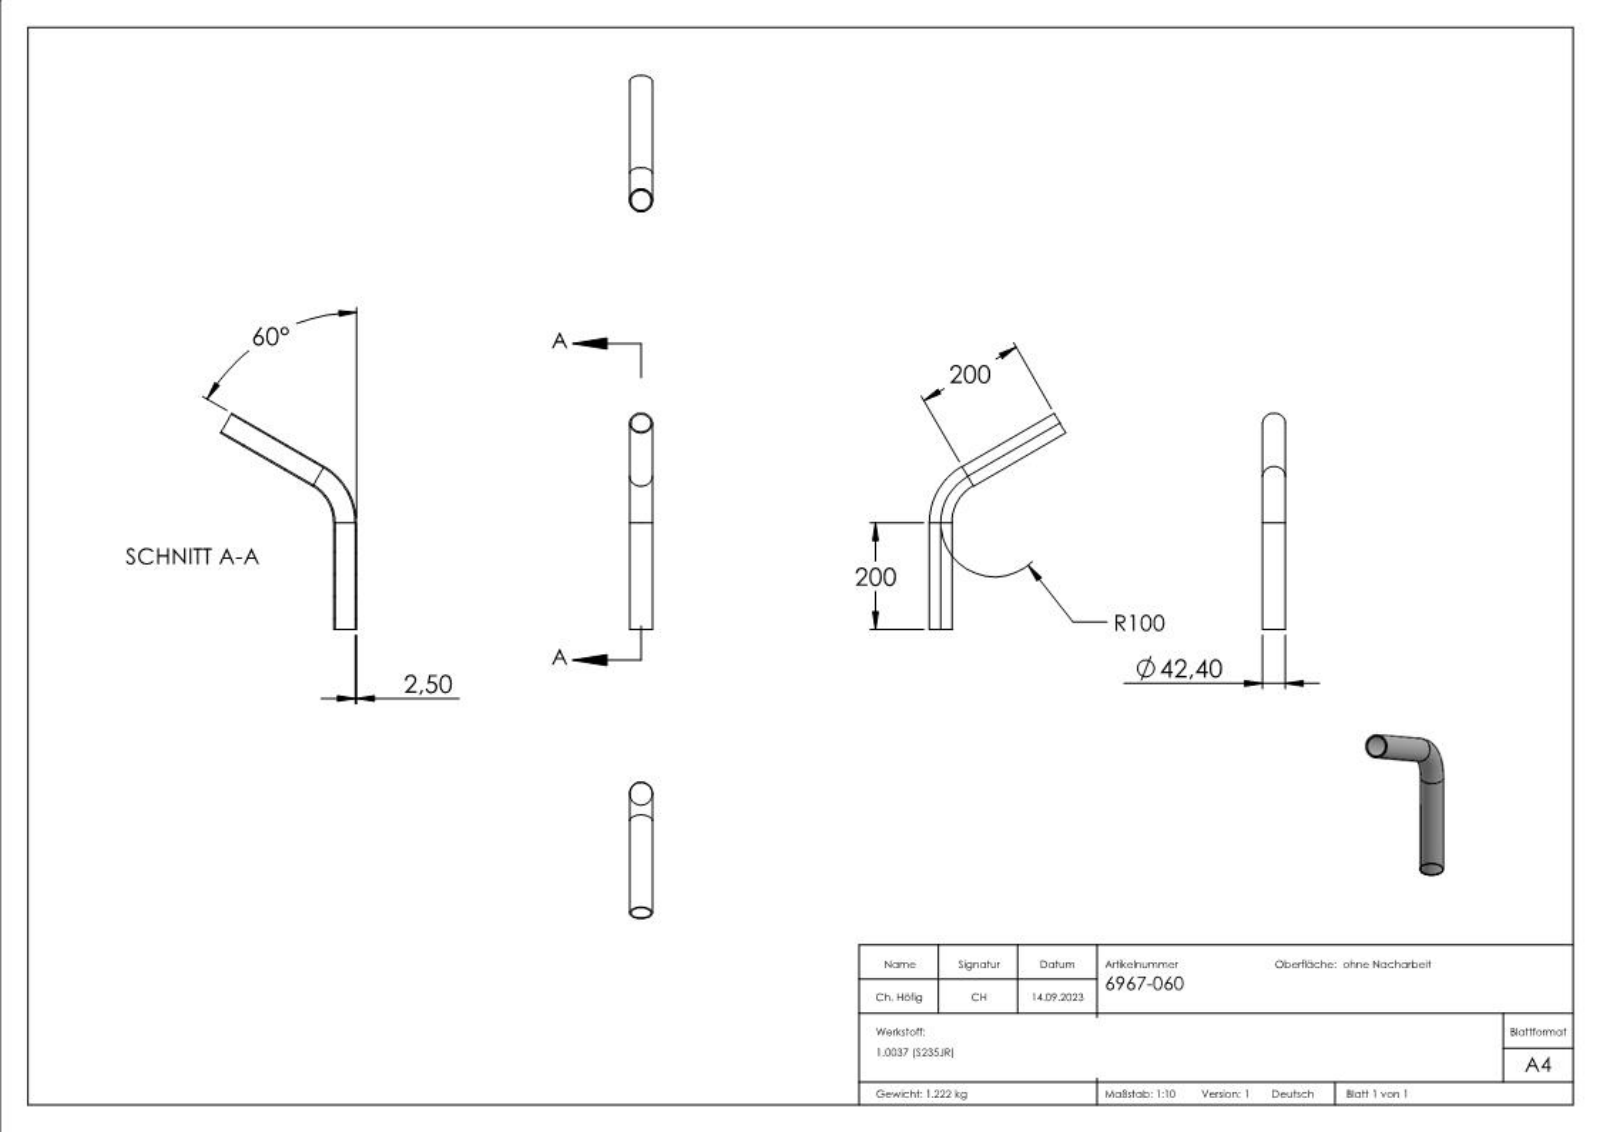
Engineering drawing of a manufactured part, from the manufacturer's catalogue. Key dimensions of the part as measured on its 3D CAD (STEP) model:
Part name (STEP PRODUCT): 6967-060
STEP written by: SolidWorks 2018 (CONFIG_CONTROL_DESIGN)
Units: millimetres
Bodies: 1 solid, 211 faces (103 planar, 4 cylindrical, 104 other)
Overall size (bounding box): 401.42 × 252.96 × 42.4
Volume: 156 687 mm³ · Surface area: 125 980 mm²
Round holes (diameter × count): ⌀37.4 ×2
Round bosses / shafts (diameter × count): ⌀42.4 ×2
Main face-to-face distances: 0.54, 0.49, 0.34, 0.53, 0.58, 0.31, 0.39, 0.48, 0.32
